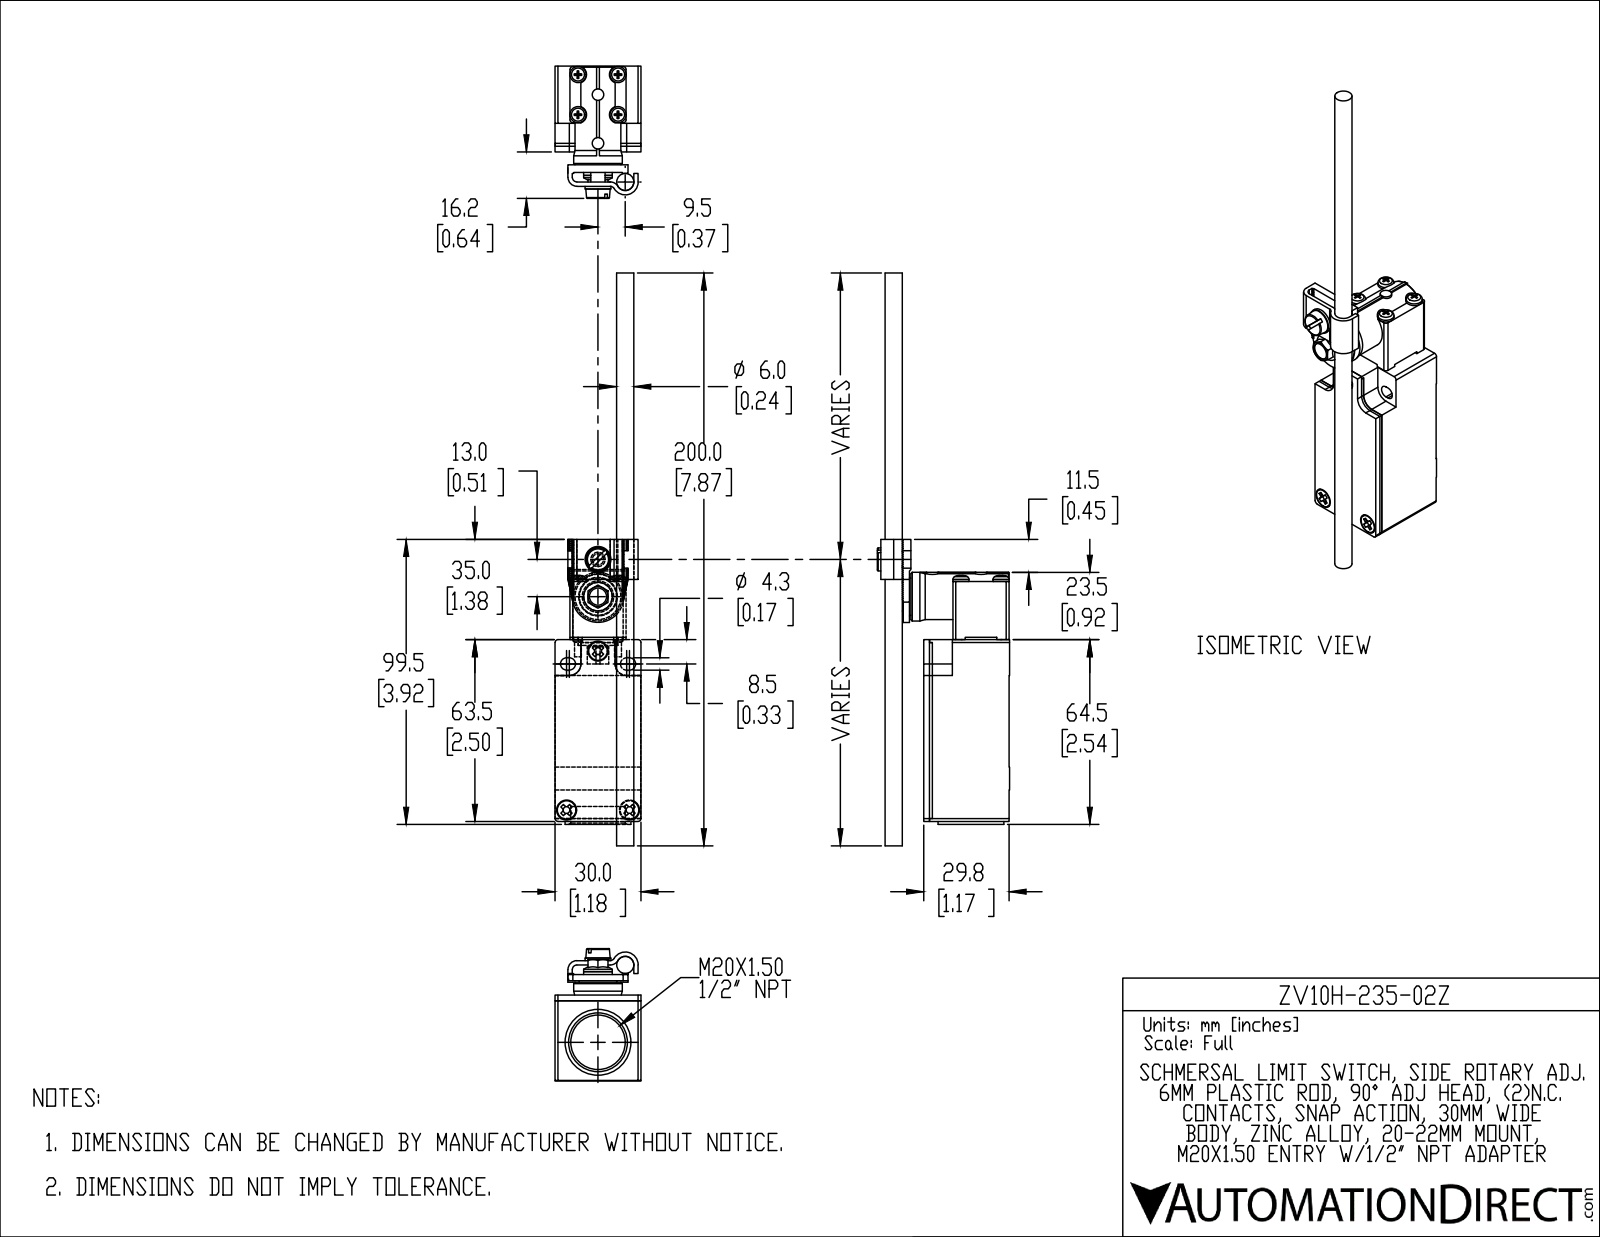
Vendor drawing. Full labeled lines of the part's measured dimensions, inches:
Part name (STEP PRODUCT): ZV10H-235-02Z
STEP written by: SolidWorks 2019 (AUTOMOTIVE_DESIGN)
Units: inches
Bodies: 2 solids, 593 faces (477 planar, 91 cylindrical, 25 other)
Overall size (bounding box): 7.874 × 1.819 × 1.181
Volume: 4.371 in³ · Surface area: 32.25 in²
Round holes (diameter × count): ⌀0.094 ×4, ⌀0.126 ×4, ⌀0.276 ×3, ⌀0.236 ×2, ⌀0.154 ×1, ⌀0.512 ×1, ⌀0.545 ×1, ⌀0.748 ×1
Round bosses / shafts (diameter × count): ⌀0.221 ×4, ⌀0.213 ×4, ⌀0.256 ×3, ⌀0.394 ×2, ⌀0.157 ×2, ⌀0.906 ×1, ⌀0.669 ×1, ⌀0.63 ×1
Partial cylindrical surfaces — rounded edges, fillets, slot ends (radius × count): R0.02 ×12, R0.039 ×8, R0.059 ×4, R0.085 ×4, R0.118 ×4, R0.063 ×2, R0.122 ×2, R0.157 ×2
Main face-to-face distances: 1.181, 1.173, 0.205, 0.976, 0.772, 0.177, 2.5, 0.281, 1.455, 1.463
Hole centre spacings: 0.39, 0.551, 0.308, 0.497, 0.78, 2.228, 2.965, 3.472
